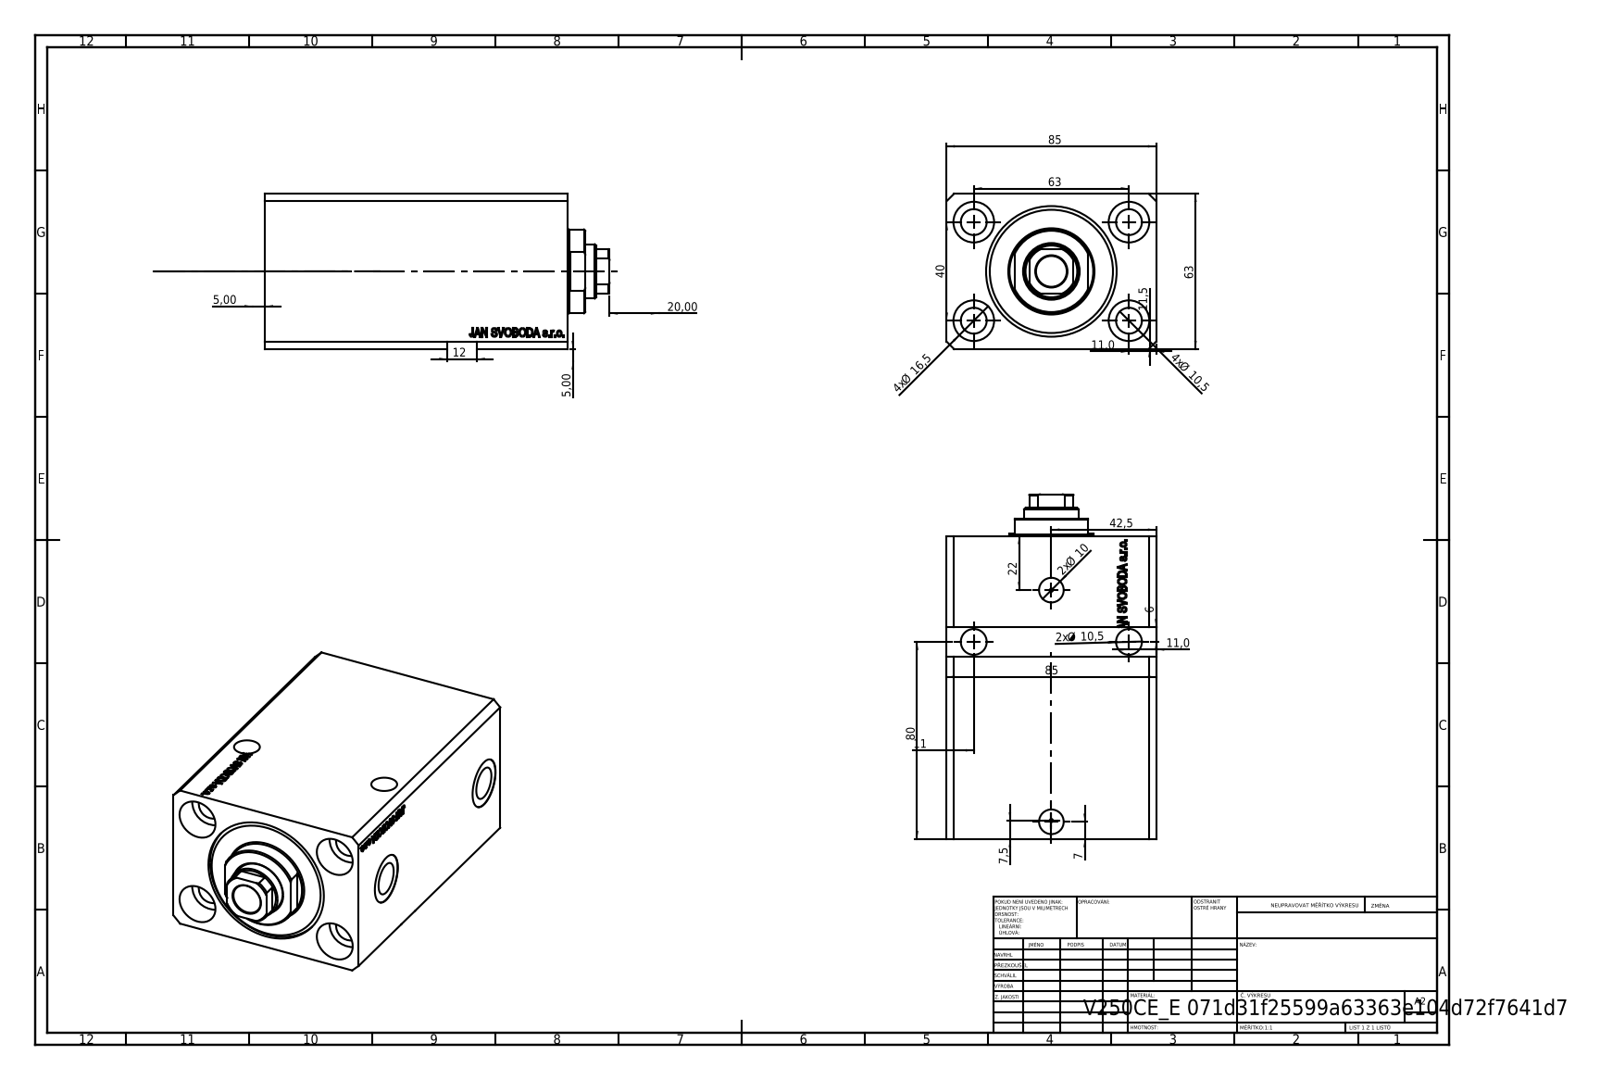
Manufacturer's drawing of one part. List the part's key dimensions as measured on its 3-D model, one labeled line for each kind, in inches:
Part name (STEP PRODUCT): V250CE_VC_E; V250CE_E_Body; V250CE_C_VCP
STEP written by: SolidWorks 2019 (CONFIG_CONTROL_DESIGN)
Units: inches
Bodies: 3 solids, 917 faces (459 planar, 84 cylindrical, 374 other)
Overall size (bounding box): 5.508 × 3.346 × 2.48
Volume: 33.6 in³ · Surface area: 167.2 in²
Round holes (diameter × count): ⌀0.413 ×6, ⌀0.049 ×4, ⌀0.65 ×4, ⌀0.394 ×2, ⌀0.518 ×2, ⌀0.787 ×2, ⌀0.492 ×1, ⌀0.866 ×1, ⌀1.575 ×1, ⌀2.087 ×1
Round bosses / shafts (diameter × count): ⌀1.339 ×1
Partial cylindrical surfaces — rounded edges, fillets, slot ends (radius × count): R0.413 ×1
Main face-to-face distances: 2.48, 3.346, 4.843, 3.776, 1.067, 3.327, 0.449, 4.394, 0.433, 4.409
Hole centre spacings: 1.469, 2.48, 1.491, 1.575, 2.938, 3.111, 3.13, 0.021
